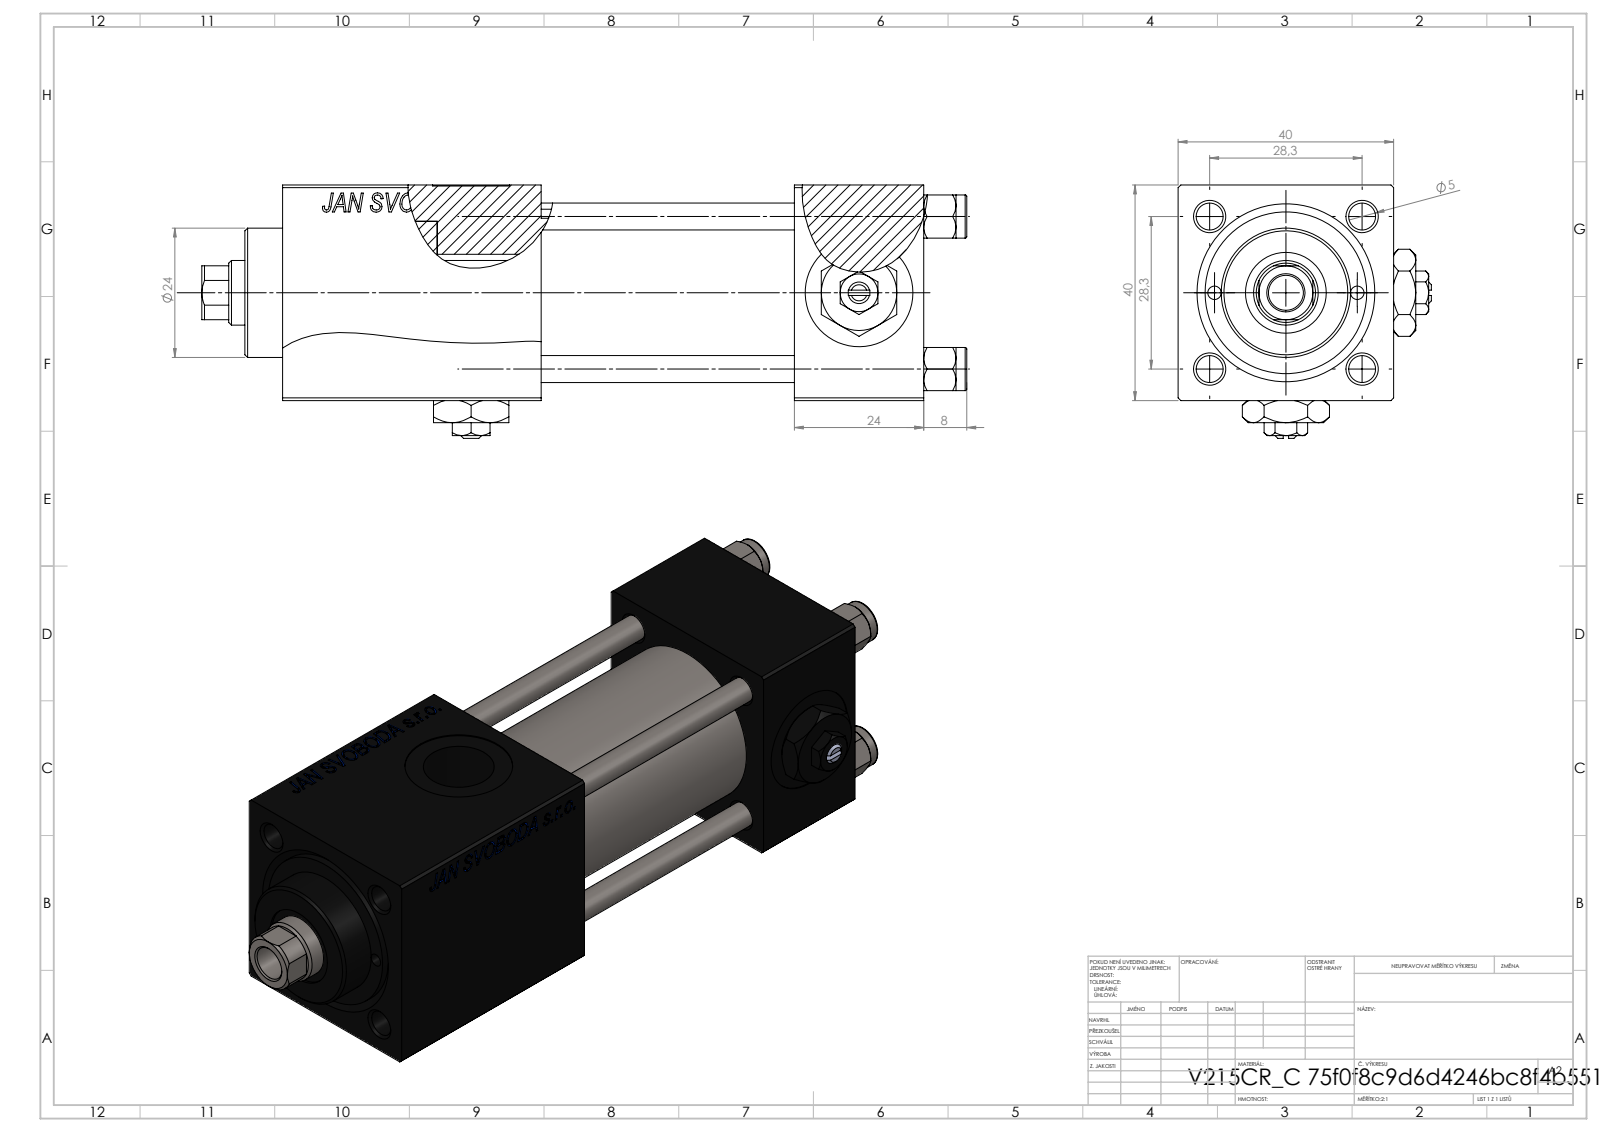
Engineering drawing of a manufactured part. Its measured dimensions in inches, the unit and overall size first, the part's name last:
Units: inches
Overall size (bounding box): 5.591 × 1.85 × 1.85
Round holes (diameter × count): ⌀0.197 ×4, ⌀0.787 ×3, ⌀0.098 ×2, ⌀0.276 ×2, ⌀0.518 ×2, ⌀0.256 ×1, ⌀0.472 ×1, ⌀0.591 ×1, ⌀0.984 ×1, ⌀1.181 ×1
Round bosses / shafts (diameter × count): ⌀0.315 ×4, ⌀1.22 ×1, ⌀0.945 ×1
Partial cylindrical surfaces — rounded edges, fillets, slot ends (radius × count): R0.217 ×1
Main face-to-face distances: 1.575, 0.945, 1.567, 3.555, 2.61, 3.74, 4.685, 1.13, 0.315, 1.063
Hole centre spacings: 0.558, 0.788, 1.114, 1.214, 0.522, 1.576, 1.043
Volume: 3.127 in³ · Surface area: 84.39 in²
Bodies: 12 solids, 1224 faces (556 planar, 101 cylindrical, 567 other)
Part name (STEP PRODUCT): V215CR_C_TYCINKA; Zatka_pro_OIL_PORT; V215CR_C_Body; V215CR_VCP_C (+2 more)
STEP written by: SolidWorks 2019 (CONFIG_CONTROL_DESIGN)
